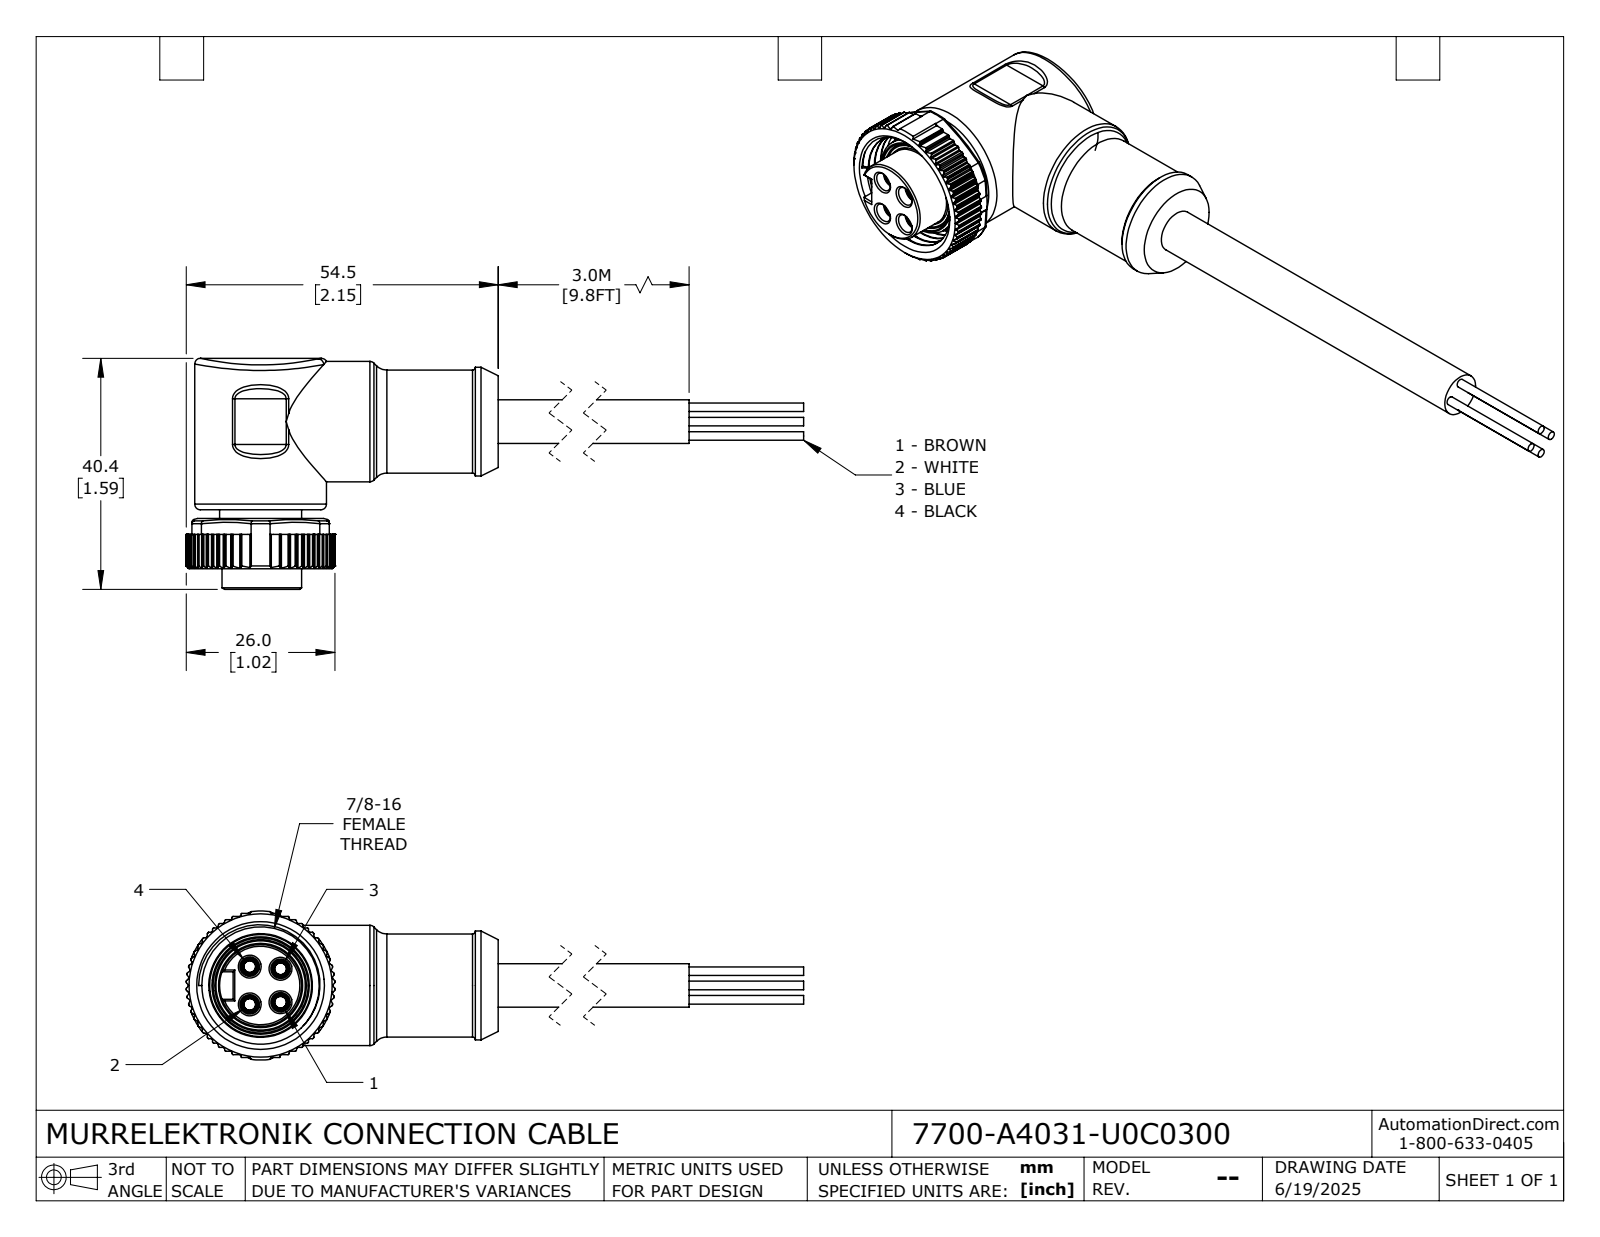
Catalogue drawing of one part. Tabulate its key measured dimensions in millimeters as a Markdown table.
| quantity | value |
| --- | --- |
| part name | 7700-A4031-U0C0300 |
| STEP written by | SolidWorks 2024 (CONFIG_CONTROL_DESIGN) |
| units | millimeters |
| bodies | 1 solid, 700 faces (294 planar, 315 cylindrical, 91 other) |
| overall size | 144.49 × 40.36 × 26 |
| volume | 26 793 mm³ |
| surface area | 9 847 mm² |
| round holes (diameter × count) | 2.05 × 4, 3 × 4, 3.4 × 4, 15.5 × 1, 15.6 × 1, 20.5 × 1, 22.23 × 1 |
| round bosses / shafts (diameter × count) | 1.5 × 4, 23 × 1, 21 × 1, 19 × 1, 18.1 × 1, 18 × 1, 17.8 × 1, 14.3 × 1 |
| partial cylindrical surfaces (radius × count) | 0.2 × 126, 0.3 × 16, 0.1 × 4, 0.73 × 4, 1 × 4, 2.5 × 4, 13 × 1, 50 × 1 |
| main face-to-face distances | 1.5, 3.6, 8.8, 10.3, 12.4, 13.9, 7.3, 3, 10.9, 21 |
| hole center spacings | 3.81, 4.54, 5.39, 8.22, 5.84, 6.6 |
